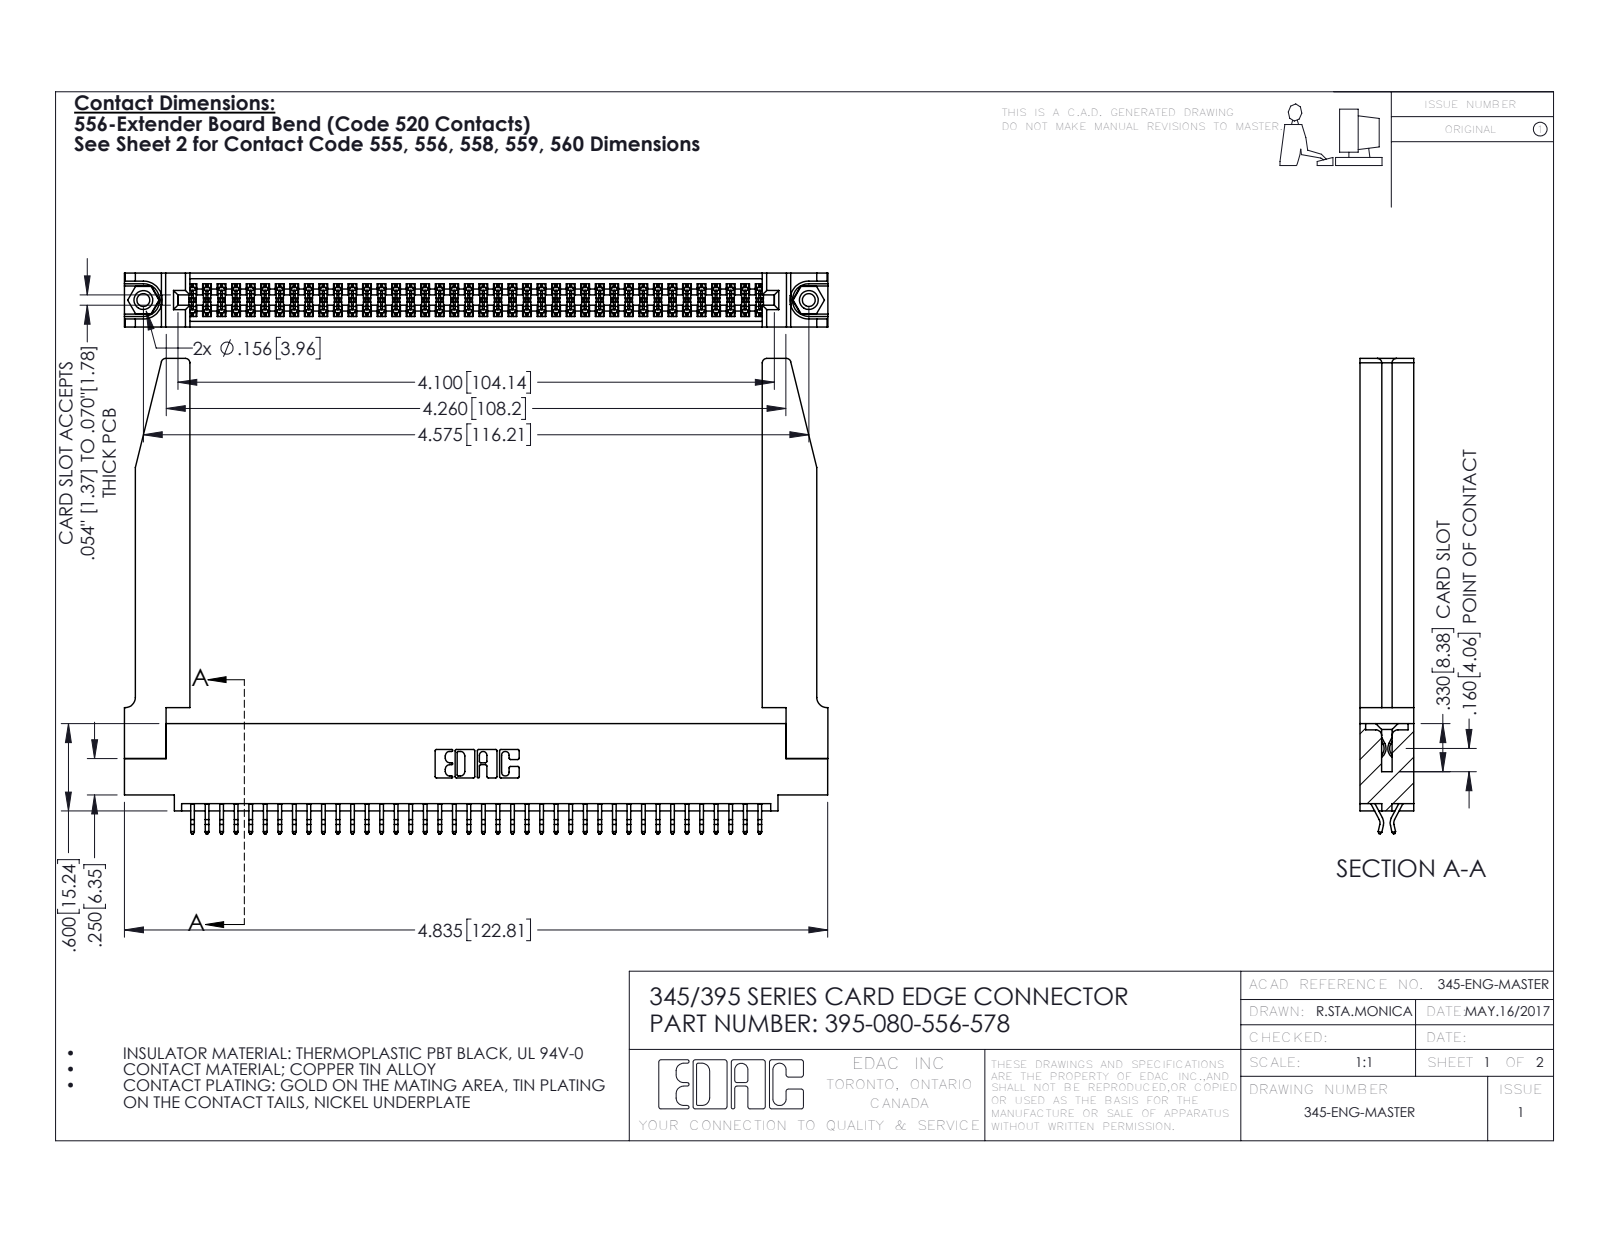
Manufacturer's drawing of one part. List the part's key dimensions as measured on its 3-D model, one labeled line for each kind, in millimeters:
Part name (STEP PRODUCT): 395-080-556-578; 345 Part_0.110 Offset - 0.156 Dia-TH; 345-292-001_556 Tail; 345-250-001_345-250-001-102 (+1 more)
STEP written by: SolidWorks 2016 (CONFIG_CONTROL_DESIGN)
Units: millimetres
Bodies: 85 solids, 4844 faces (3186 planar, 1606 cylindrical, 52 other)
Overall size (bounding box): 122.8 × 83 × 9.4
Volume: 19 620 mm³ · Surface area: 24 320 mm²
Round holes (diameter × count): ⌀2.3 ×2, ⌀3.2 ×2, ⌀4 ×2, ⌀1.6 ×1
Round bosses / shafts (diameter × count): ⌀3.9 ×2
Partial cylindrical surfaces — rounded edges, fillets, slot ends (radius × count): R0.2 ×120, R0.3 ×22, R0.8 ×8, R0.2 ×6, R0.8 ×6, R0.7 ×3, R0.3 ×2, R0.4 ×2
Main face-to-face distances: 9.4, 1.8, 7.6, 0.6, 5.1, 2.5, 6.9, 5.7, 3.8, 3.8
Hole centre spacings: 6.9, 110.2, 116.2
